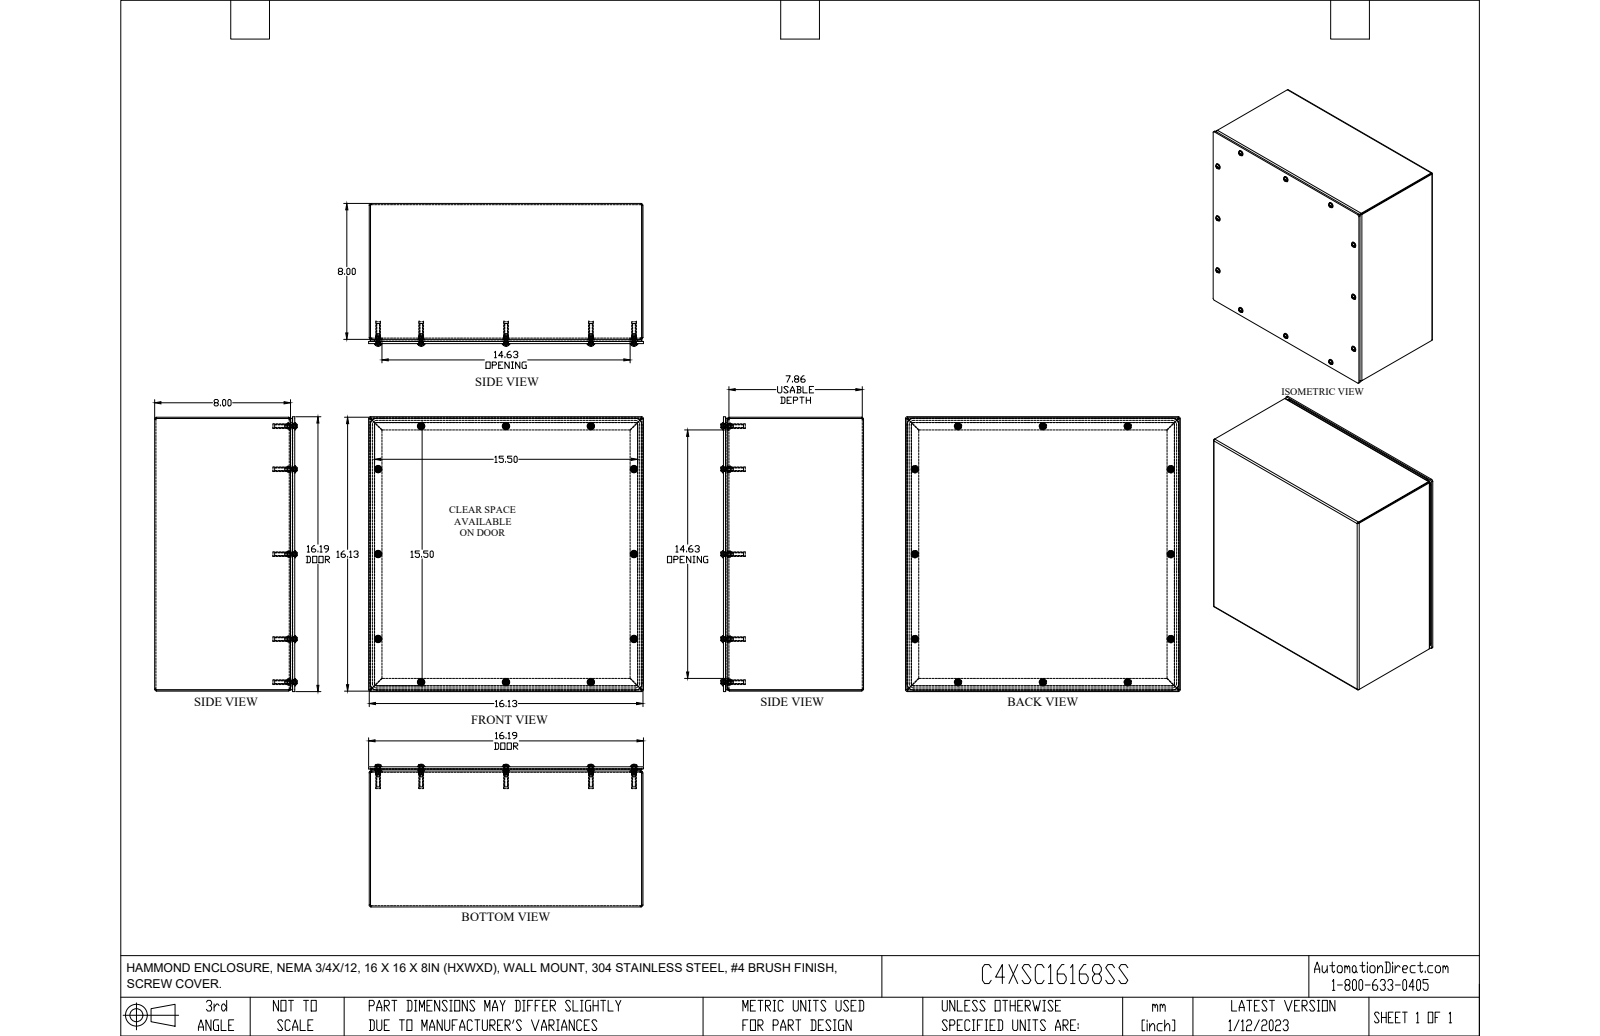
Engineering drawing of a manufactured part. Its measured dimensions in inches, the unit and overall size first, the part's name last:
Units: inches
Overall size (bounding box): 16.188 × 16.188 × 8.4
Round holes (diameter × count): ⌀0.159 ×12, ⌀0.16 ×12, ⌀0.25 ×12
Round bosses / shafts (diameter × count): ⌀0.44 ×12, ⌀0.39 ×12, ⌀0.24 ×12, ⌀0.19 ×12, ⌀0.148 ×12, ⌀0.275 ×10, ⌀0.275 ×2
Partial cylindrical surfaces — rounded edges, fillets, slot ends (radius × count): R0.16 ×12, R0.036 ×8, R0.04 ×8, R0.108 ×8, R0.11 ×8, R0.125 ×8, R0.126 ×4, R0.374 ×4
Main face-to-face distances: 0.072, 0.07, 16.053, 8.125, 0.125, 8.25, 8.18, 8.055, 8.178, 8.053
Hole centre spacings: 5, 7.953, 12.792, 14.629, 15.882, 15.075, 3.589, 10
Volume: 149.3 in³ · Surface area: 3 873 in²
Bodies: 40 solids, 1278 faces (810 planar, 228 cylindrical, 240 other)
Part name (STEP PRODUCT): C3SC16168GY
STEP written by: SolidWorks 2021 (AUTOMOTIVE_DESIGN)
